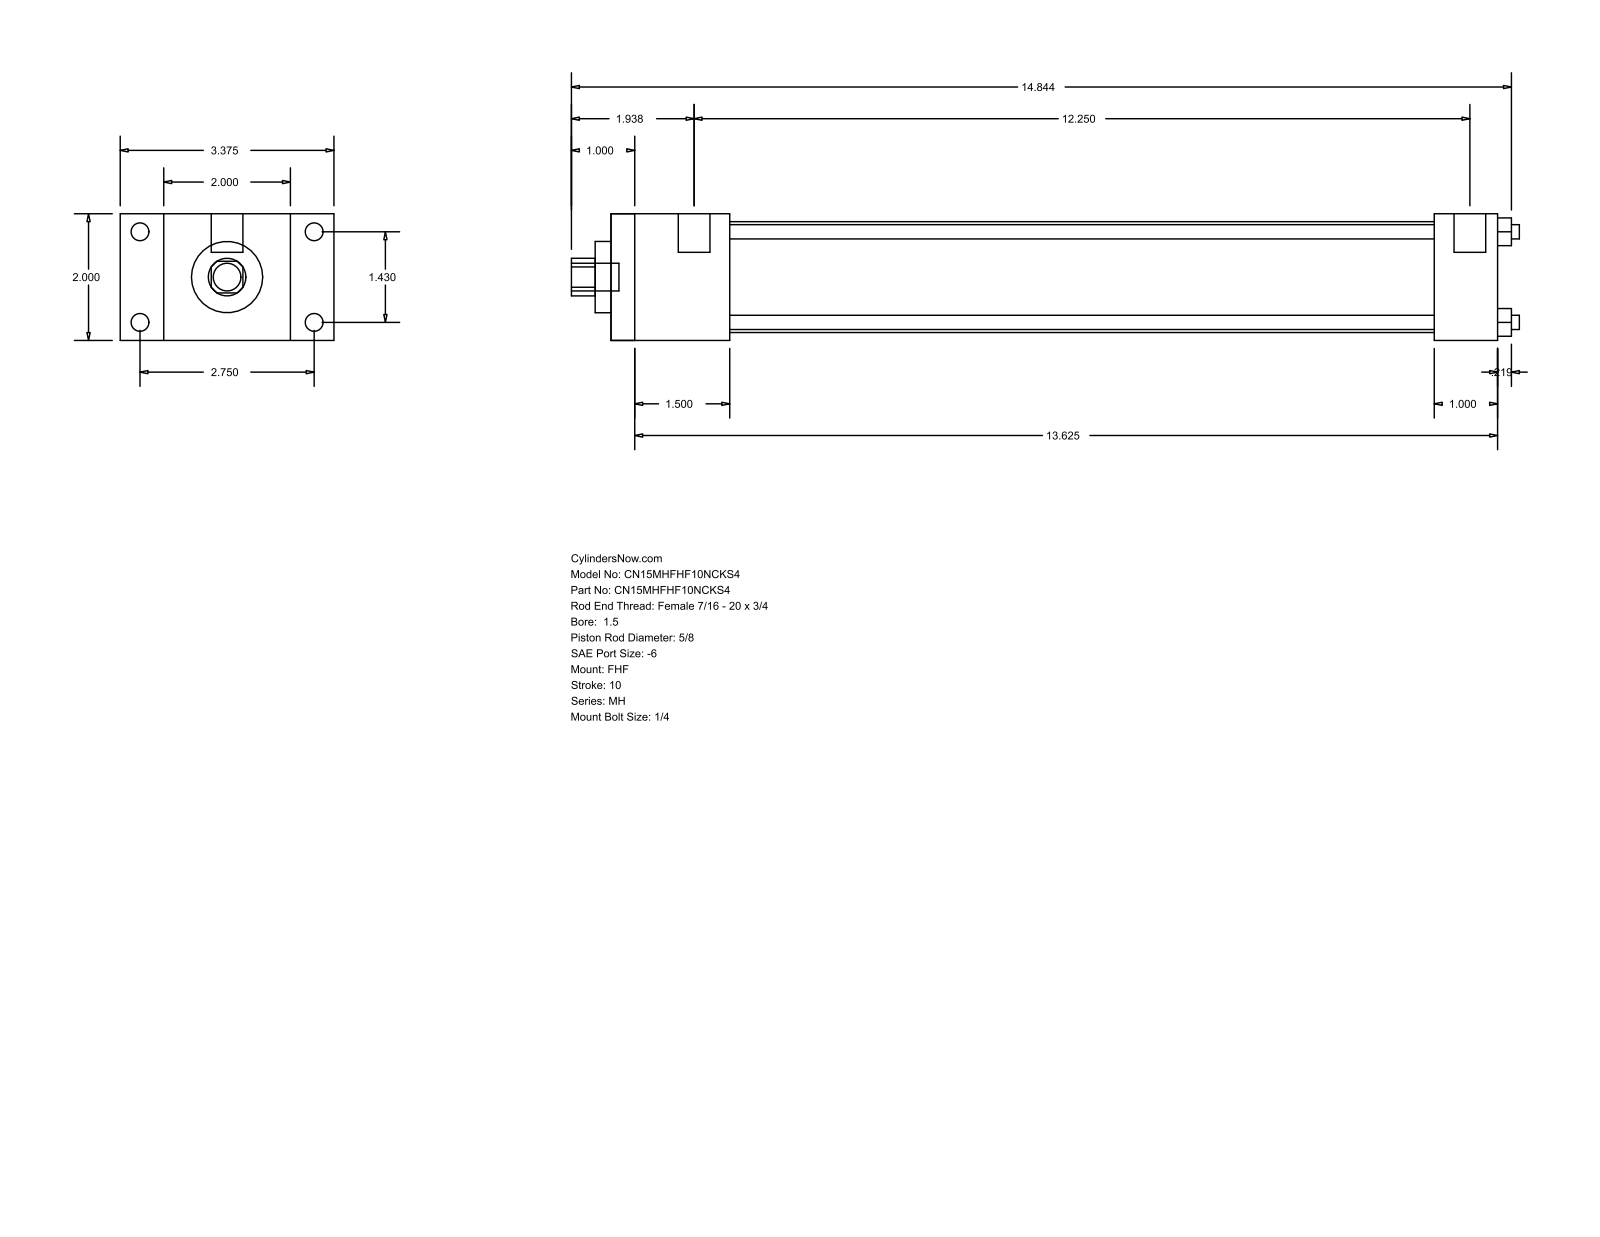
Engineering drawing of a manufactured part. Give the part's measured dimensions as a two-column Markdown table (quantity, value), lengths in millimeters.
| quantity | value |
| --- | --- |
| part name | MH_FHF__0150_0.625 |
| STEP written by | GSSL Pune (CONFIG_CONTROL_DESIGN) |
| units | millimeters |
| bodies | 0 solids, 88 faces (60 planar, 28 cylindrical, 0 other) |
| overall size | 380.21 × 85.72 × 50.8 |
| round holes (diameter × count) | 5.71 × 4, 15.88 × 1, 28.57 × 1, 44.45 × 1 |
| round bosses / shafts (diameter × count) | 7.14 × 4, 5.56 × 4, 12.7 × 2, 11.11 × 1 |
| partial cylindrical surfaces (radius × count) | 7.54 × 1 |
| main face-to-face distances | 50.8, 17.46, 68.26, 47.62, 85.72, 355.6, 307.98, 330.19, 282.57, 25.41 |
| hole center spacings | 25.68, 36.32, 51.36 |
